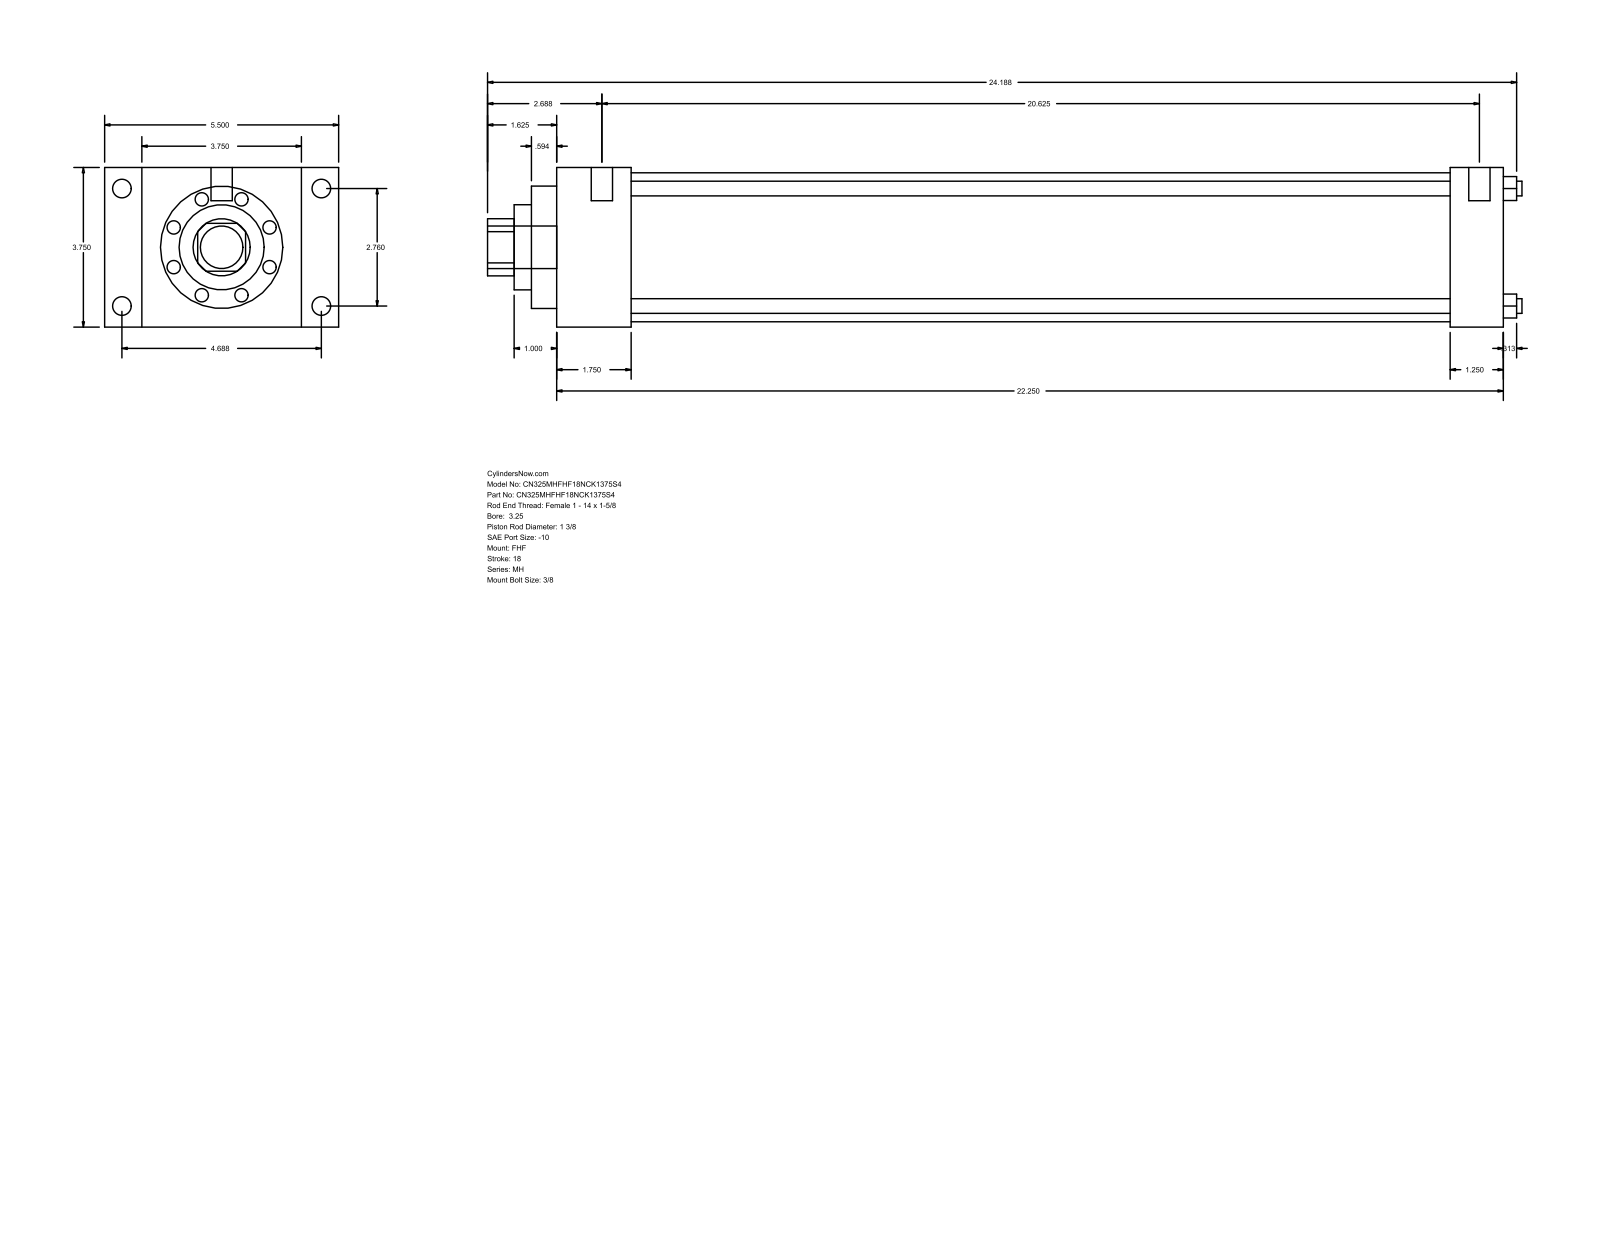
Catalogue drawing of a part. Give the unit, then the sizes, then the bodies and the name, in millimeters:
Units: millimetres
Overall size (bounding box): 617.54 × 139.7 × 95.25
Round holes (diameter × count): ⌀8.76 ×4, ⌀34.92 ×1, ⌀50.8 ×1, ⌀73.03 ×1, ⌀88.9 ×1
Round bosses / shafts (diameter × count): ⌀11.13 ×4, ⌀5.56 ×4, ⌀12.7 ×2, ⌀25.4 ×1
Partial cylindrical surfaces — rounded edges, fillets, slot ends (radius × count): R17.06 ×1
Main face-to-face distances: 95.24, 565.15, 44.45, 520.7, 22.23, 117.47, 139.7, 533.4, 488.95, 31.75
Hole centre spacings: 49.57, 70.1, 99.14
Bodies: 0 solids, 90 faces (61 planar, 29 cylindrical, 0 other)
Part name (STEP PRODUCT): MH_FHF__0325_1.375
STEP written by: GSSL Pune (CONFIG_CONTROL_DESIGN)
